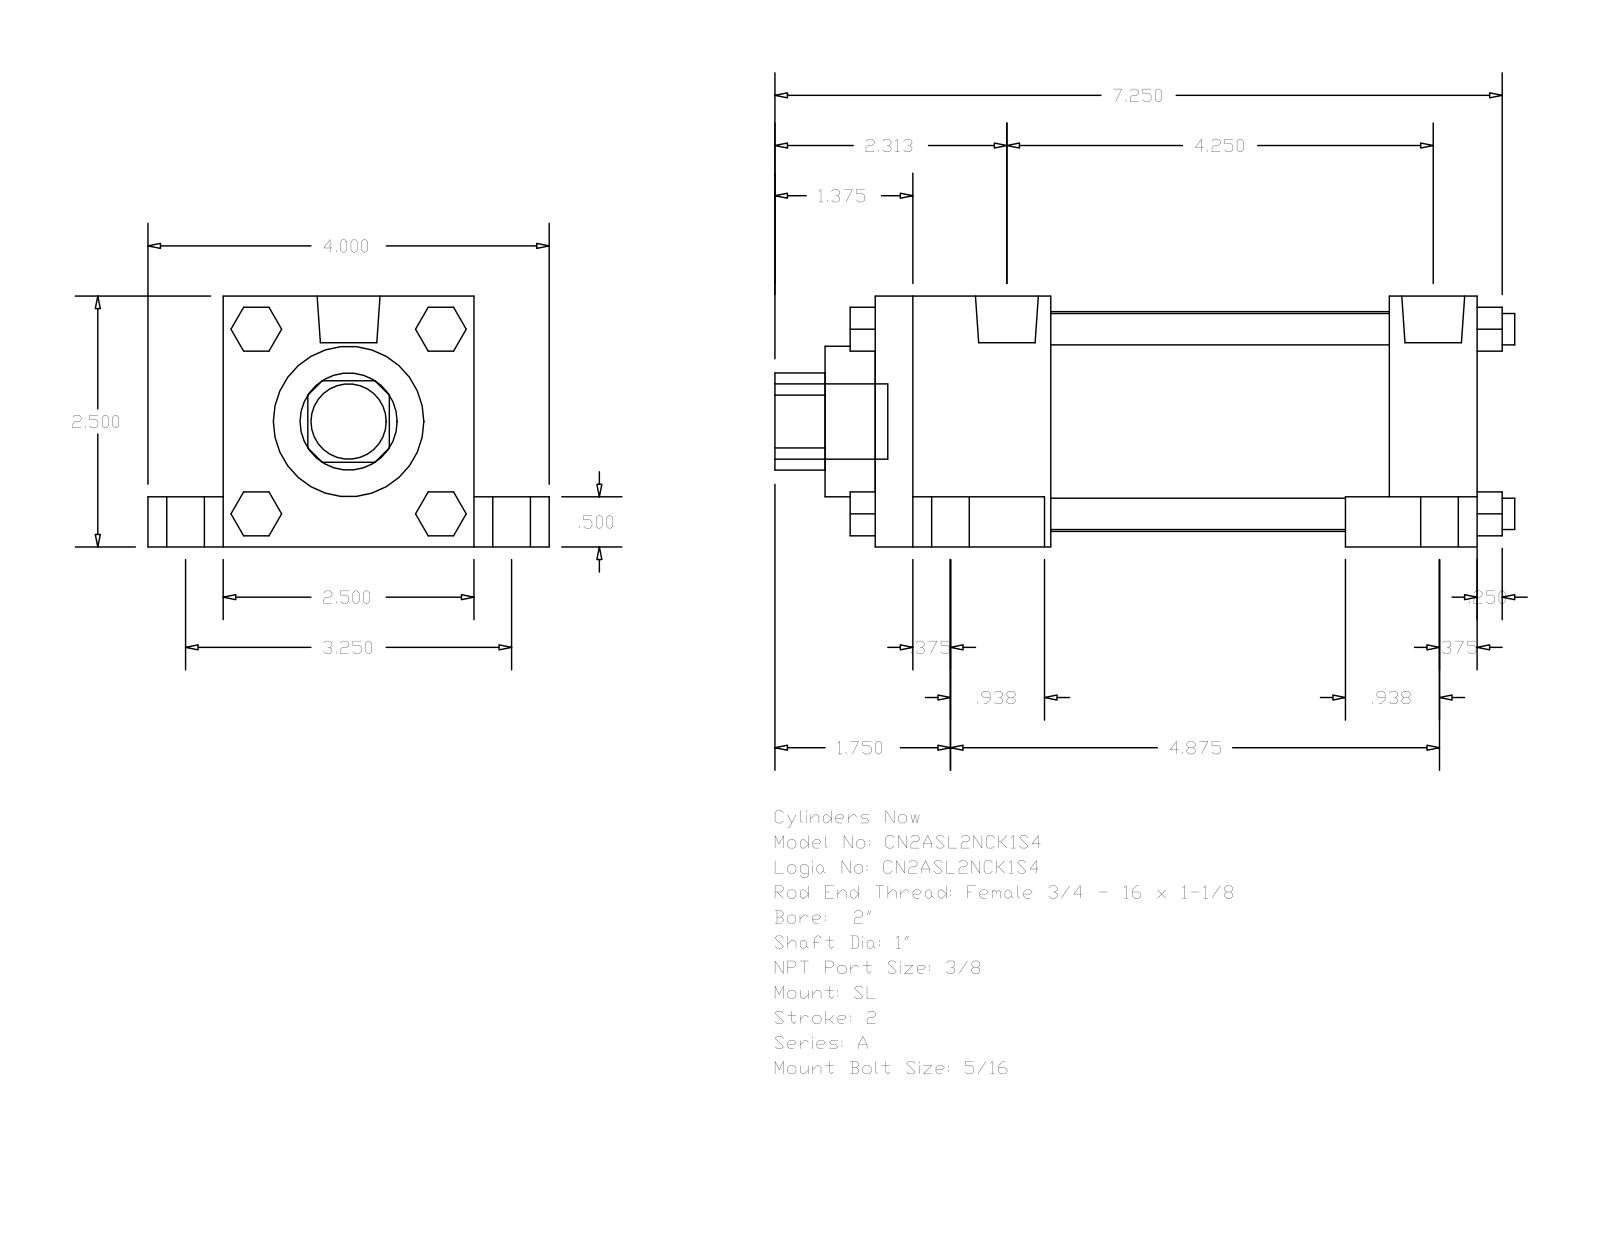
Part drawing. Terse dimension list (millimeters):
name: A_SL__0200_1
written by: GSSL Pune (CONFIG_CONTROL_DESIGN)
unit: mm
bodies: 0 solids, 148 faces (112 planar, 36 cylindrical, 0 other)
size: 187.32 × 101.6 × 63.5
holes: 1× ⌀25.4, 1× ⌀38.1, 1× ⌀55.63
bosses: 4× ⌀15.88, 4× ⌀9.53, 4× ⌀7.94, 4× ⌀5.56, 2× ⌀15.93, 1× ⌀19.05
rounds: 1× R12.29
face distances: 63.5, 152.4, 12.7, 50.8, 19.05, 82.55, 9.52, 44.45, 107.95, 130.17
